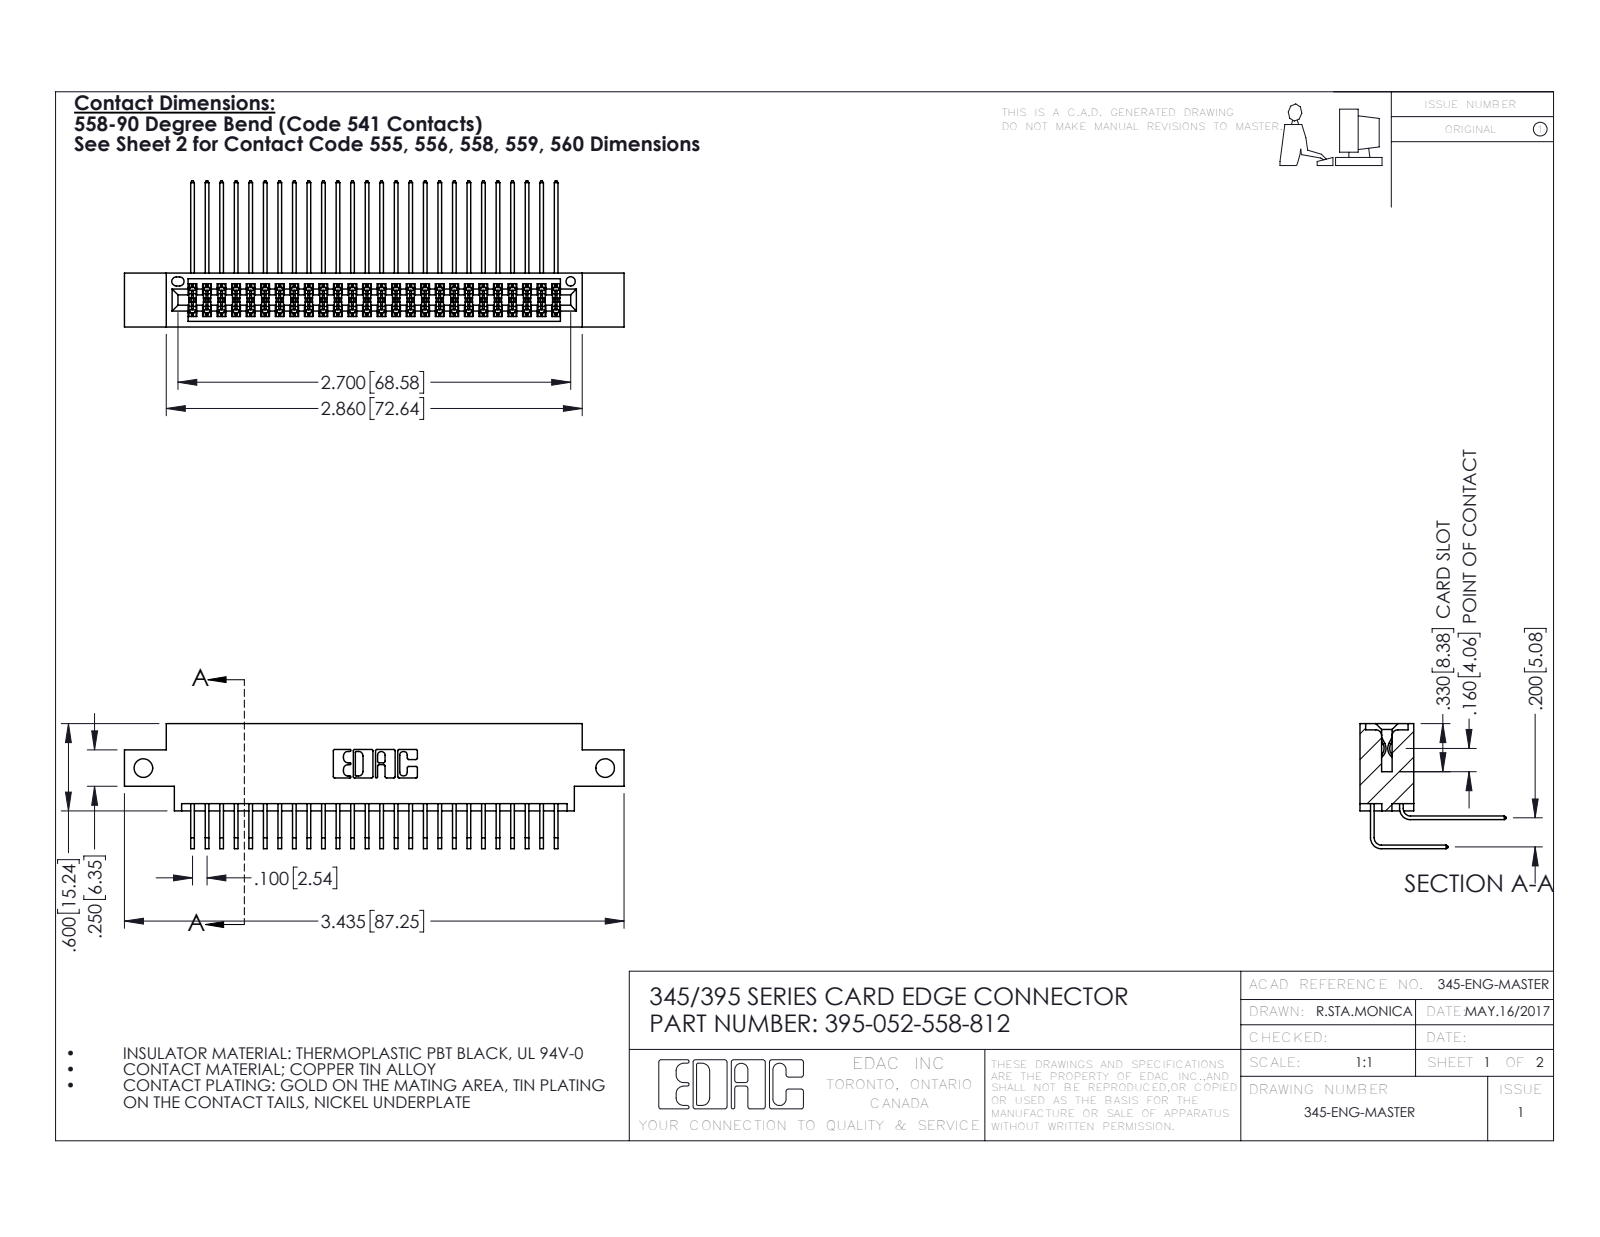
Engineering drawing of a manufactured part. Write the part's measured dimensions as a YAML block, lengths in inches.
part_name: "345 Part_0.170 Offset - Side Mount; 395-052-558-812; 345-292-001_558 559 Tail - 1; 345-292-001_558 Tail - 2"
step_written_by: "SolidWorks 2016 (CONFIG_CONTROL_DESIGN)"
units: inches
bodies: {solids: 53, faces: 2834, planar: 1904, cylindrical: 930, other: 0}
overall_size: [3.435, 1.005, 0.859]
volume: 0.514
surface_area: 21.02
round_holes:
  - {diameter: 0.128, count: 2}
  - {diameter: 0.064, count: 1}
partial_cylinders:
  - {radius: 0.006, count: 79}
  - {radius: 0.01, count: 22}
  - {radius: 0.007, count: 6}
  - {radius: 0.031, count: 6}
  - {radius: 0.026, count: 3}
  - {radius: 0.014, count: 2}
  - {radius: 0.019, count: 2}
  - {radius: 0.022, count: 2}
face_to_face_distances: [0.072, 0.298, 0.2, 0.37, 0.098, 0.272, 0.025, 0.225, 0.175, 0.025]
hole_center_spacings: [3.175]
